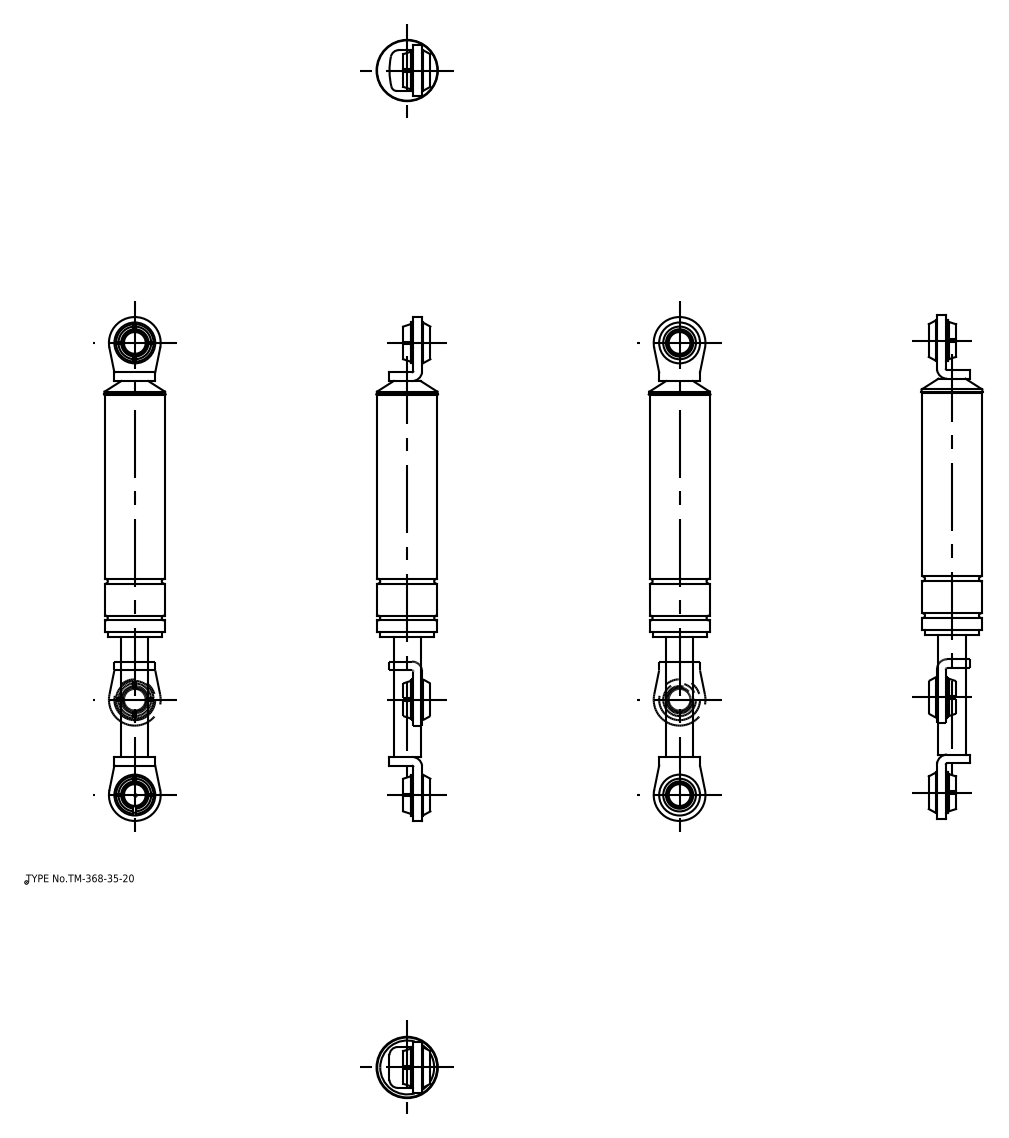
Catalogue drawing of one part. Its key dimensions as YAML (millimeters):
part_name: "TM_368_35_20; TM_368_35_20_div"
step_written_by: "spGate 16.7.1 (AUTOMOTIVE_DESIGN)"
units: millimeters
bodies: {solids: 2, faces: 155, planar: 76, cylindrical: 37, other: 42}
overall_size: [185, 22.5, 22.5]
volume: 42089
surface_area: 11995
round_holes:
  - {diameter: 8, count: 2}
round_bosses_or_shafts:
  - {diameter: 15, count: 2}
  - {diameter: 13, count: 2}
  - {diameter: 22, count: 1}
  - {diameter: 19.8, count: 1}
  - {diameter: 10, count: 1}
partial_cylinders:
  - {radius: 3, count: 3}
  - {radius: 0.5, count: 2}
  - {radius: 3.7, count: 2}
  - {radius: 9.5, count: 2}
  - {radius: 2, count: 1}
  - {radius: 25, count: 1}
face_to_face_distances: [3.2, 7, 141.2, 4.25, 3, 47.2, 2.75, 144.4, 97.2, 7.25]
hole_center_spacings: [166]
